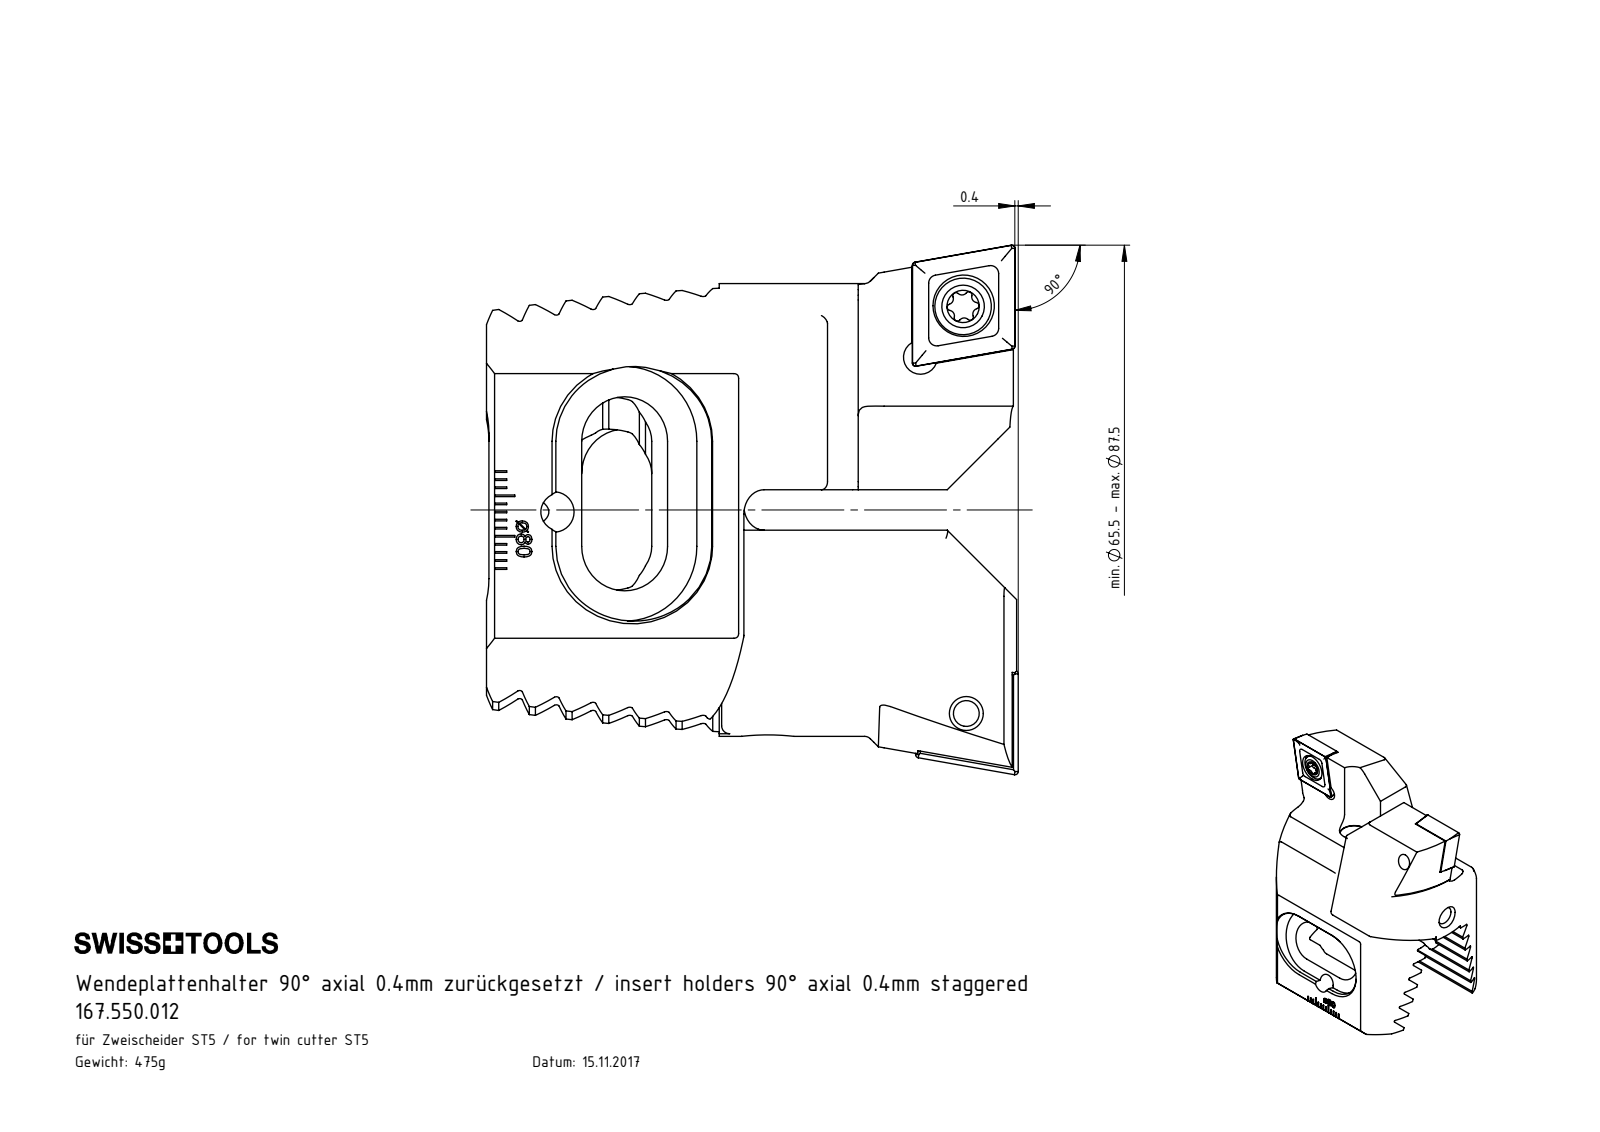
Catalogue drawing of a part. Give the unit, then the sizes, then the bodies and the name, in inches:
Units: inches
Overall size (bounding box): 2.591 × 2.539 × 1.736
Round holes (diameter × count): ⌀0.165 ×4, ⌀0.079 ×3, ⌀0.217 ×2, ⌀0.299 ×2, ⌀0.039 ×1, ⌀0.197 ×1
Round bosses / shafts (diameter × count): ⌀0.276 ×2, ⌀0.197 ×2, ⌀0.236 ×1, ⌀0.157 ×1
Partial cylindrical surfaces — rounded edges, fillets, slot ends (radius × count): R0.015 ×12, R0.039 ×11, R0.013 ×6, R0.013 ×6, R0.027 ×6, R0.027 ×6, R0.118 ×5, R0.217 ×4
Main face-to-face distances: 0.16, 0.32, 0.481, 0.641, 0.801, 0.199, 1.736, 0.176, 0.171, 0.335
Hole centre spacings: 0.157, 0.315, 0.323, 0.326, 0.328, 0.335, 0.591, 0.63
Volume: 3.766 in³ · Surface area: 35.43 in²
Bodies: 8 solids, 560 faces (250 planar, 137 cylindrical, 173 other)
Part name (STEP PRODUCT): Z55-WCC.001.037_A; CCMT120404; WCC-ER2.001.010_A; Z55-xxx.001.037_C_versetzt (+3 more)
STEP written by: SolidWorks 2017 (CONFIG_CONTROL_DESIGN)
